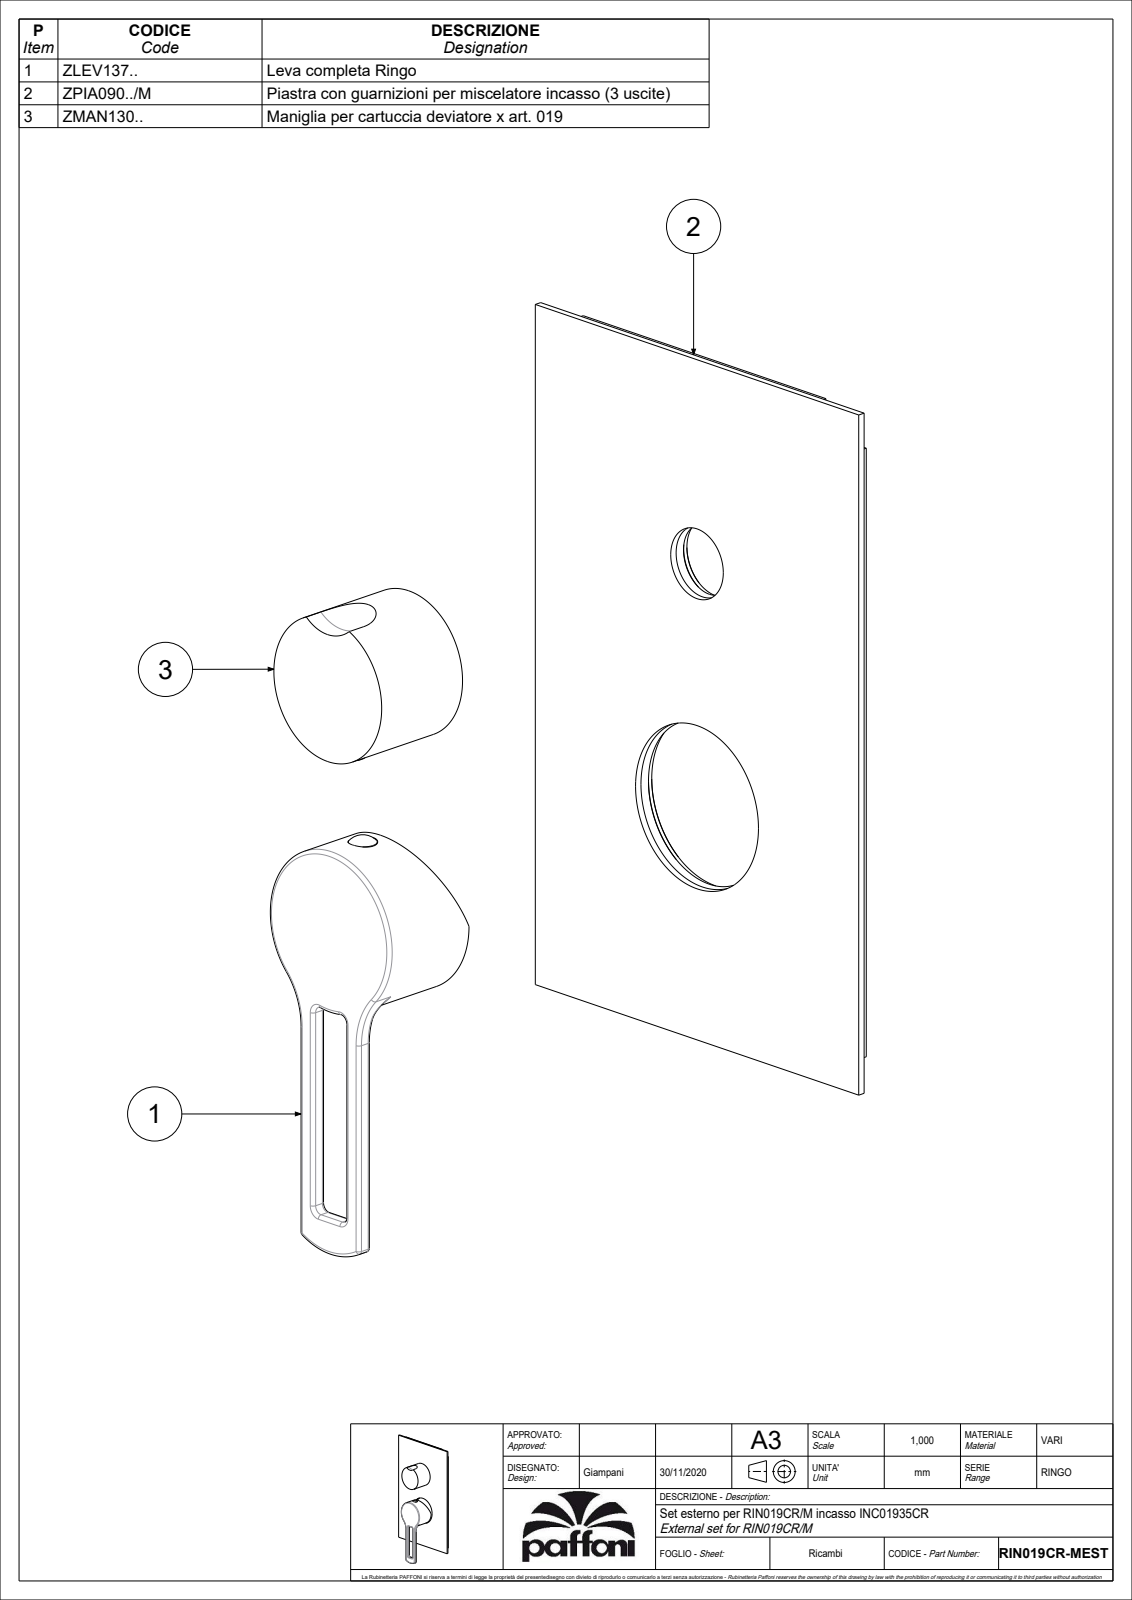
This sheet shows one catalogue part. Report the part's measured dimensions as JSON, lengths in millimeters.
{"part_name": "RIN018CR-MEST", "step_written_by": "CREO PARAMETRIC BY PTC INC, 2020044 (CONFIG_CONTROL_DESIGN)", "units": "millimeters", "bodies": {"solids": 3, "faces": 336, "planar": 108, "cylindrical": 108, "other": 120}, "overall_size": [215, 120, 39.85], "volume_mm3": 91175, "surface_area_mm2": 72379, "round_holes": [[3, 2], [3.2, 1], [4.2, 1], [7.8, 1], [14.8, 1], [19.5, 1], [21.5, 1], [25, 1], [36, 1], [45.6, 1], [47.6, 1], [51.1, 1]], "round_bosses_or_shafts": [[7.6, 2], [5.5, 2], [54.6, 1], [44.8, 1], [40, 1], [28.5, 1], [24, 1], [5, 1]], "partial_cylinders_radius": [[1, 12], [0.5, 8], [2, 4], [20, 2], [12.5, 1], [21.67, 1]], "face_to_face_distances": [2, 0.8, 2.8, 34.3, 33.5, 31.5, 39, 4.5, 29.8, 29], "hole_center_spacings": [3, 10, 68, 78]}
